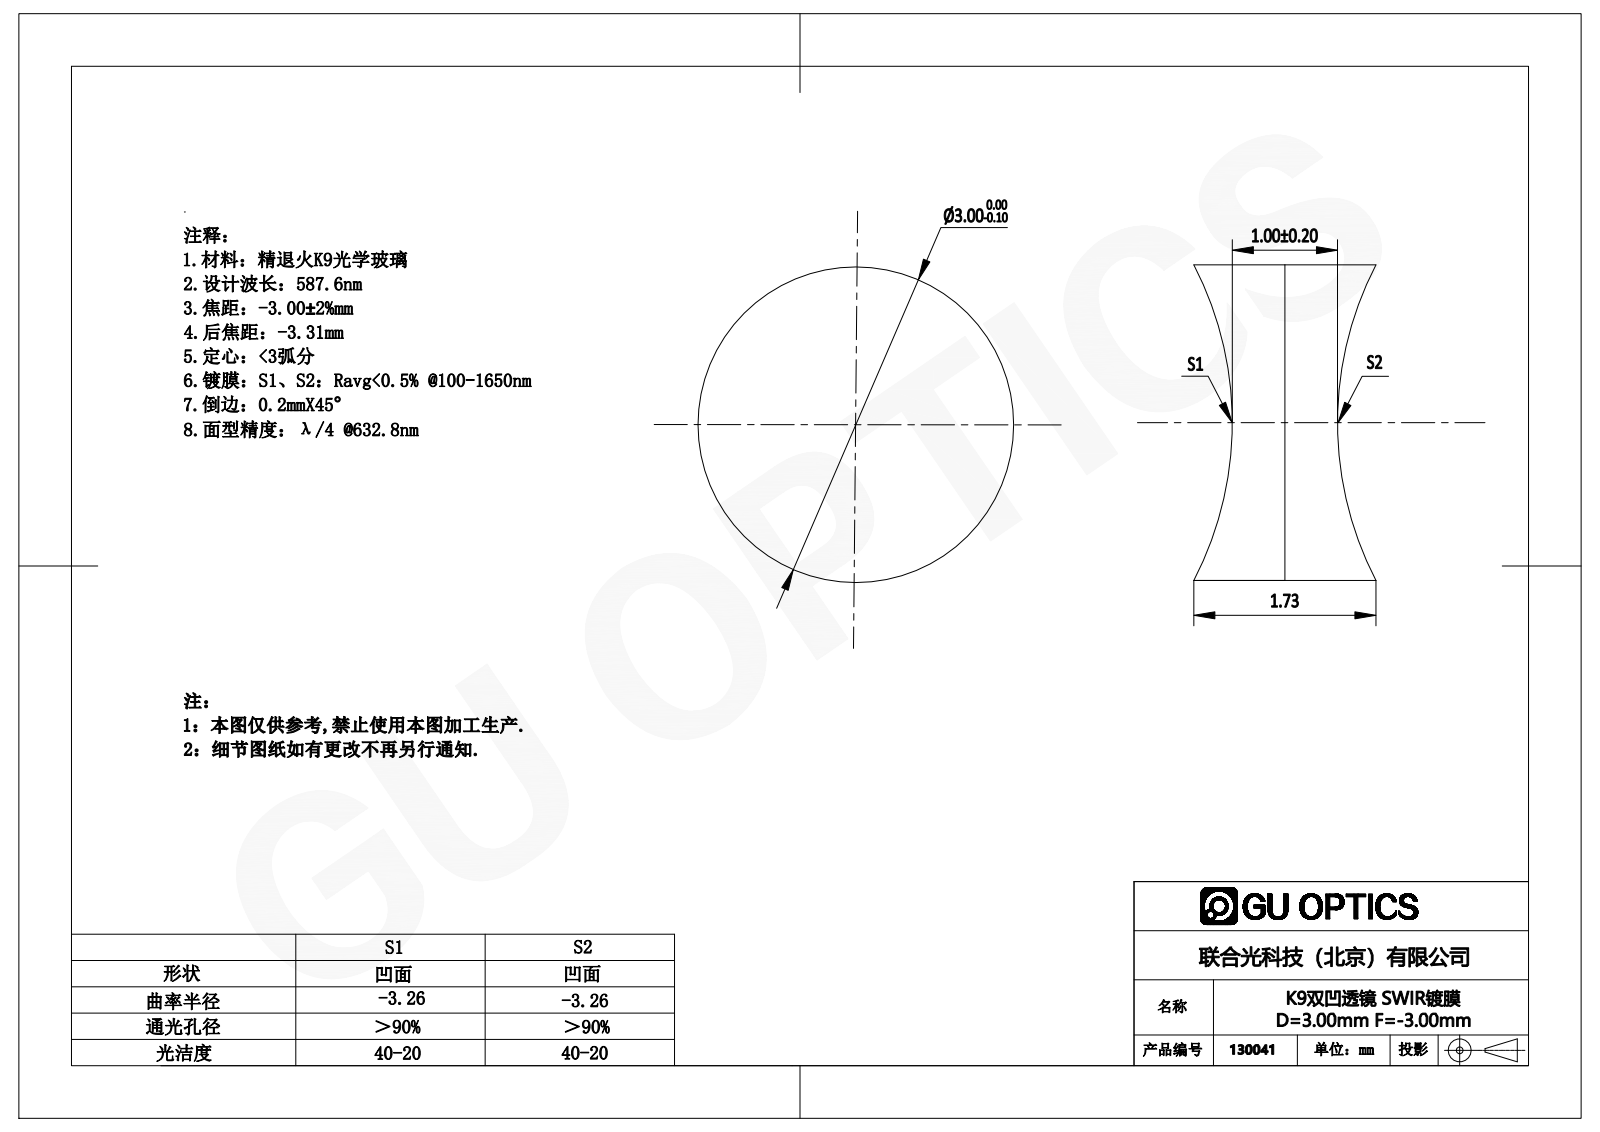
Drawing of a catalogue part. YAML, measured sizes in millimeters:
part_name: "130002"
step_written_by: "SolidWorks 2016 (AUTOMOTIVE_DESIGN)"
units: millimeters
bodies: {solids: 1, faces: 6, planar: 0, cylindrical: 2, other: 4}
overall_size: [3, 3, 1.73]
volume: 10
surface_area: 31
round_bosses_or_shafts:
  - {diameter: 3, count: 1}
